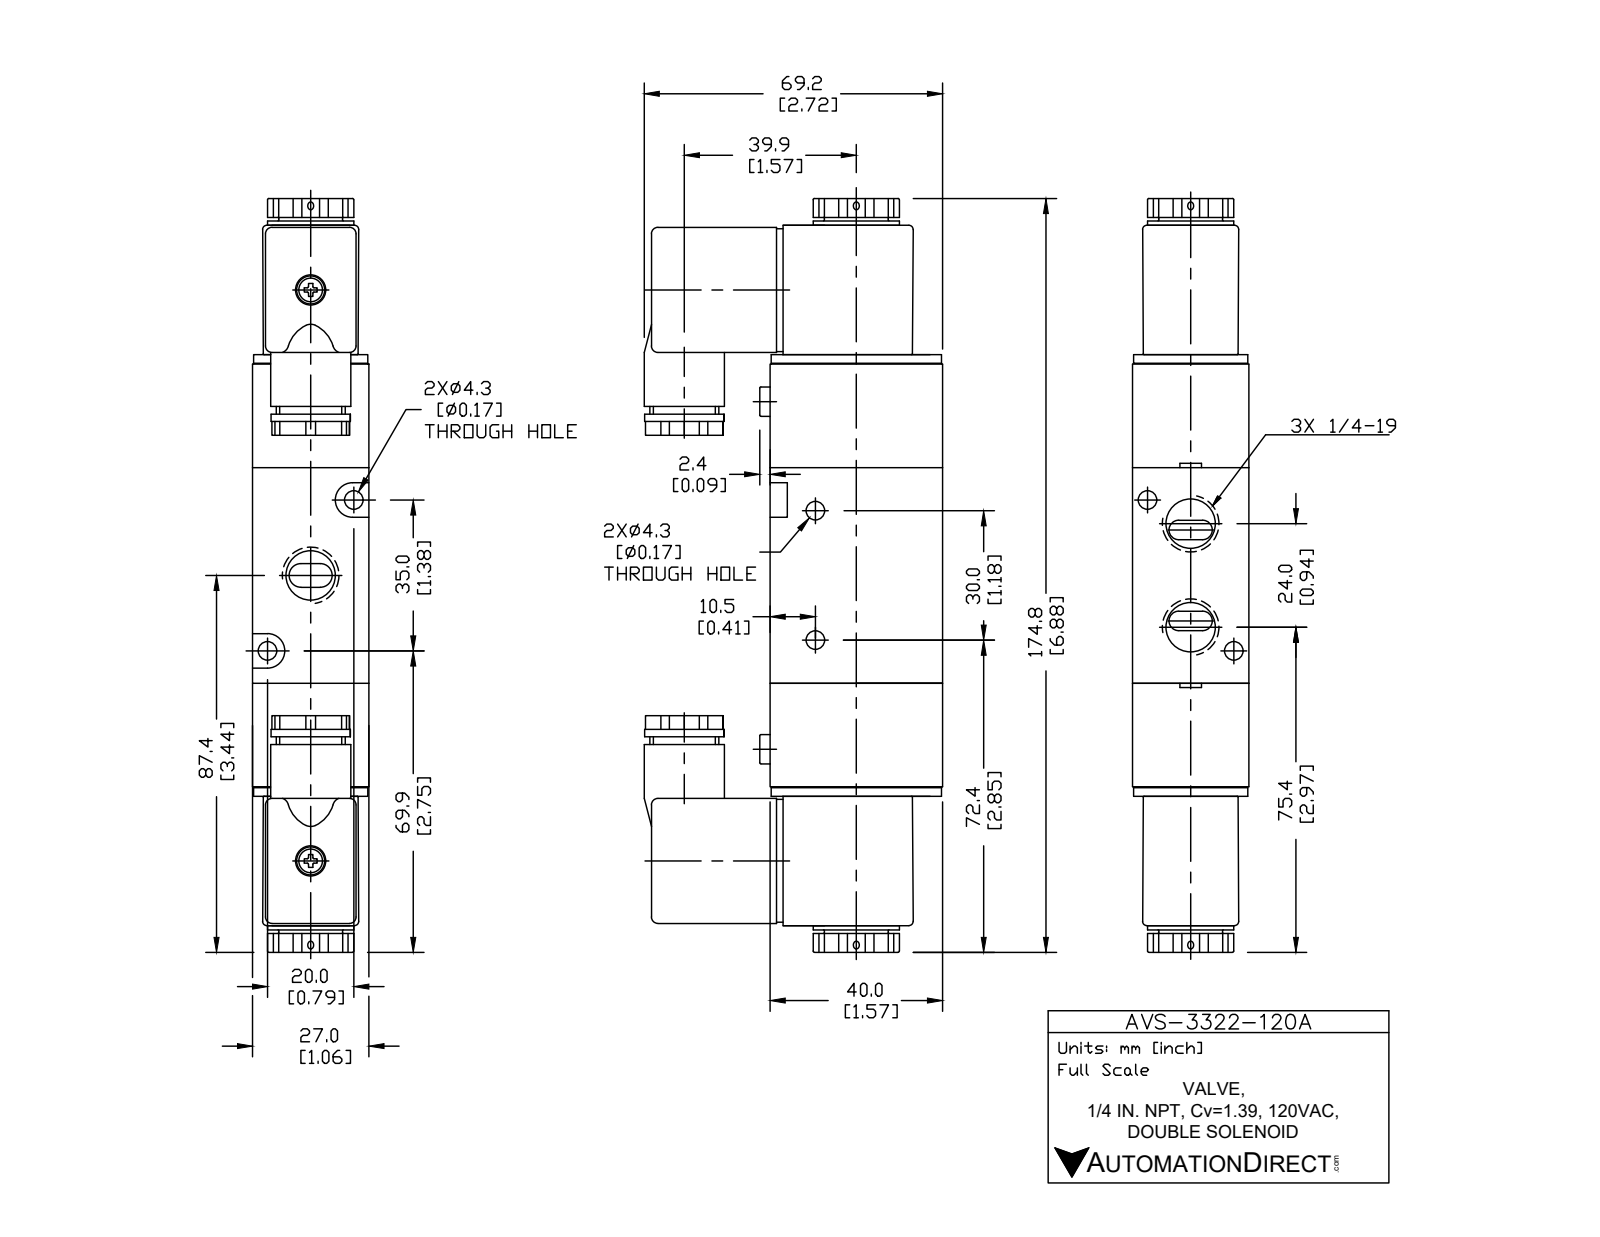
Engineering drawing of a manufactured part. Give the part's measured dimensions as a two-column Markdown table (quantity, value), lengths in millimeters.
| quantity | value |
| --- | --- |
| part name | AVS-3322-120A |
| STEP written by | SolidWorks 2015 (CONFIG_CONTROL_DESIGN) |
| units | millimeters |
| bodies | 5 solids, 246 faces (132 planar, 82 cylindrical, 32 other) |
| overall size | 174.8 × 69.1 × 27 |
| volume | 190 787 mm³ |
| surface area | 40 116 mm² |
| round holes (diameter × count) | 4.3 × 4, 11.13 × 3, 9.3 × 1 |
| round bosses / shafts (diameter × count) | 6.8 × 2, 20 × 1, 18.6 × 1, 18.4 × 1, 16 × 1, 14.8 × 1 |
| partial cylindrical surfaces (radius × count) | 1 × 20, 0.5 × 12, 4 × 2 |
| main face-to-face distances | 3, 24, 50, 27.45, 27, 21, 25.19, 2.26, 2.27, 22.92 |
| hole center spacings | 11.41, 12.09, 31.15, 19.46, 20.94, 24, 30, 40.31 |
